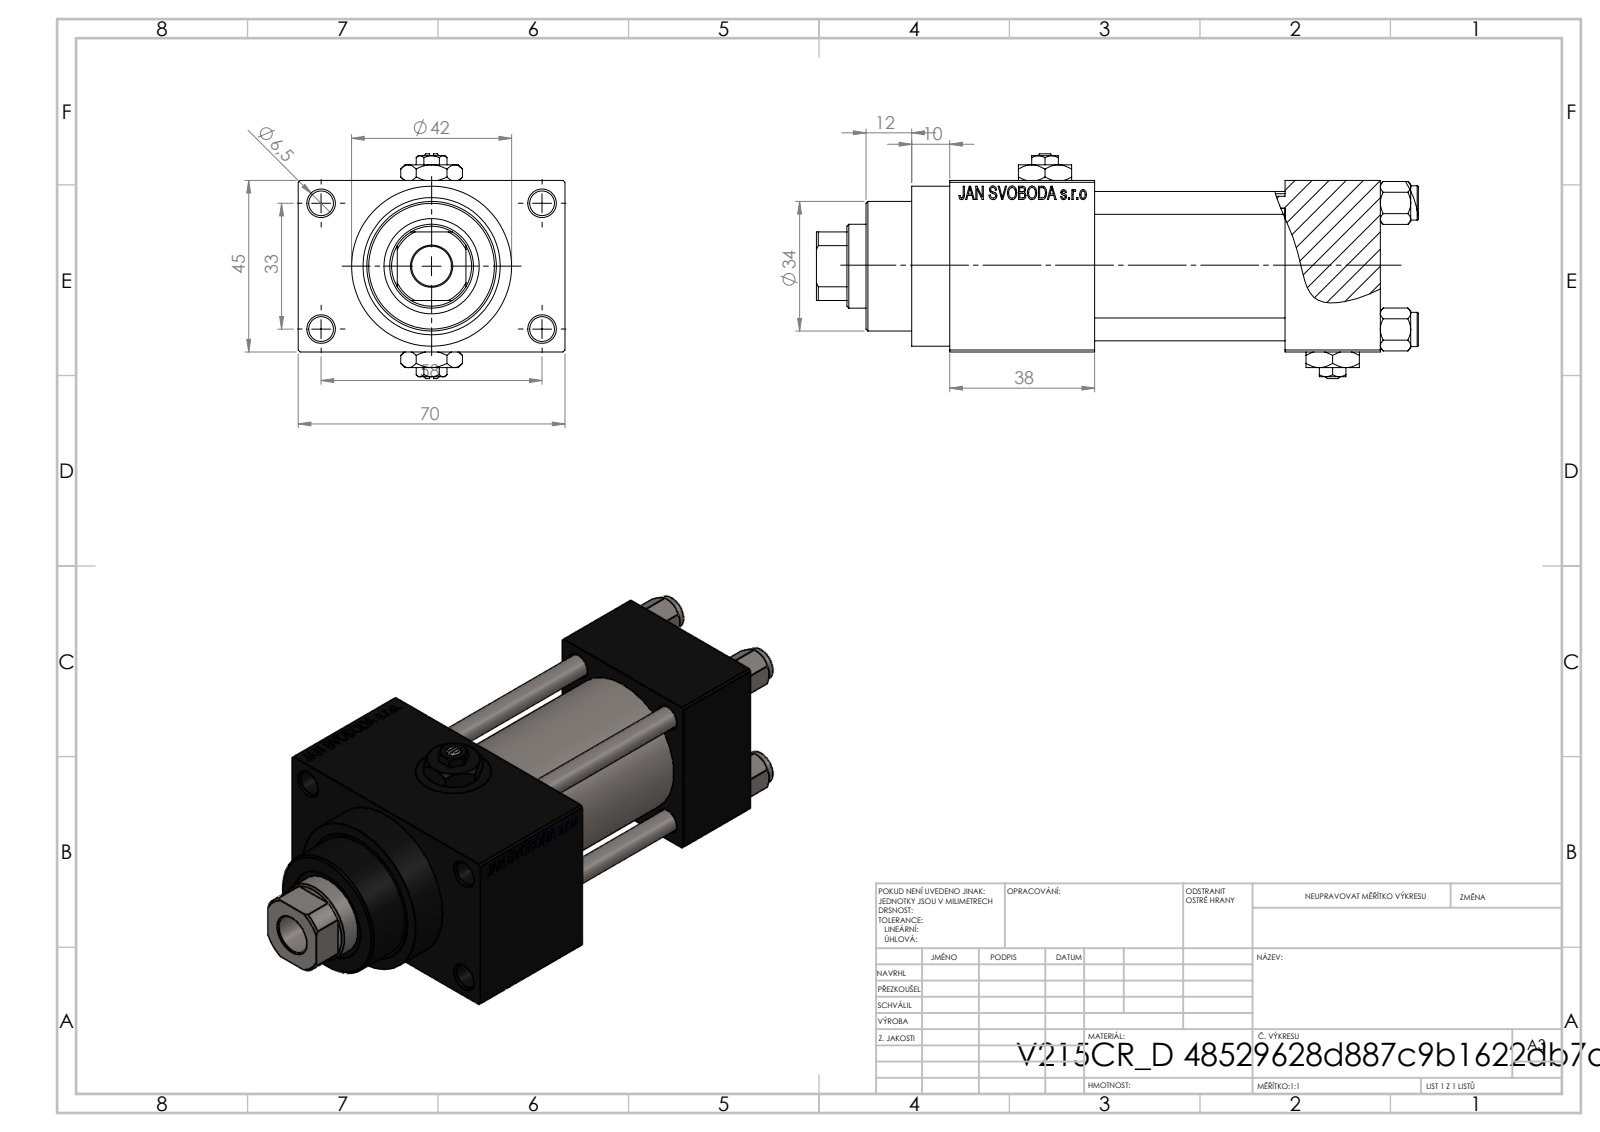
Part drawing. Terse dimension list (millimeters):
name: V215CR_D_Body; V215_VC_A; NUT_M5_D; Zatka_pro_OIL_PORT (+2 more)
written by: SolidWorks 2019 (CONFIG_CONTROL_DESIGN)
unit: mm
bodies: 13 solids, 1189 faces (540 planar, 89 cylindrical, 560 other)
size: 158 × 70 × 59
volume: 246 146 mm³; area: 80 557 mm²
holes: 4× ⌀6, 4× ⌀6.5, 2× ⌀7, 2× ⌀13.16, 2× ⌀20, 1× ⌀10.5, 1× ⌀22, 1× ⌀24, 1× ⌀25, 1× ⌀32, 1× ⌀33
bosses: 4× ⌀9, 1× ⌀42, 1× ⌀38, 1× ⌀34
rounds: 1× R10.5
face distances: 45, 25, 12.5, 57.5, 50, 75, 88, 70, 38, 113
hole spacings: 12.4, 23.48, 33.2, 33.37, 35.35, 45.6, 56.35, 33
